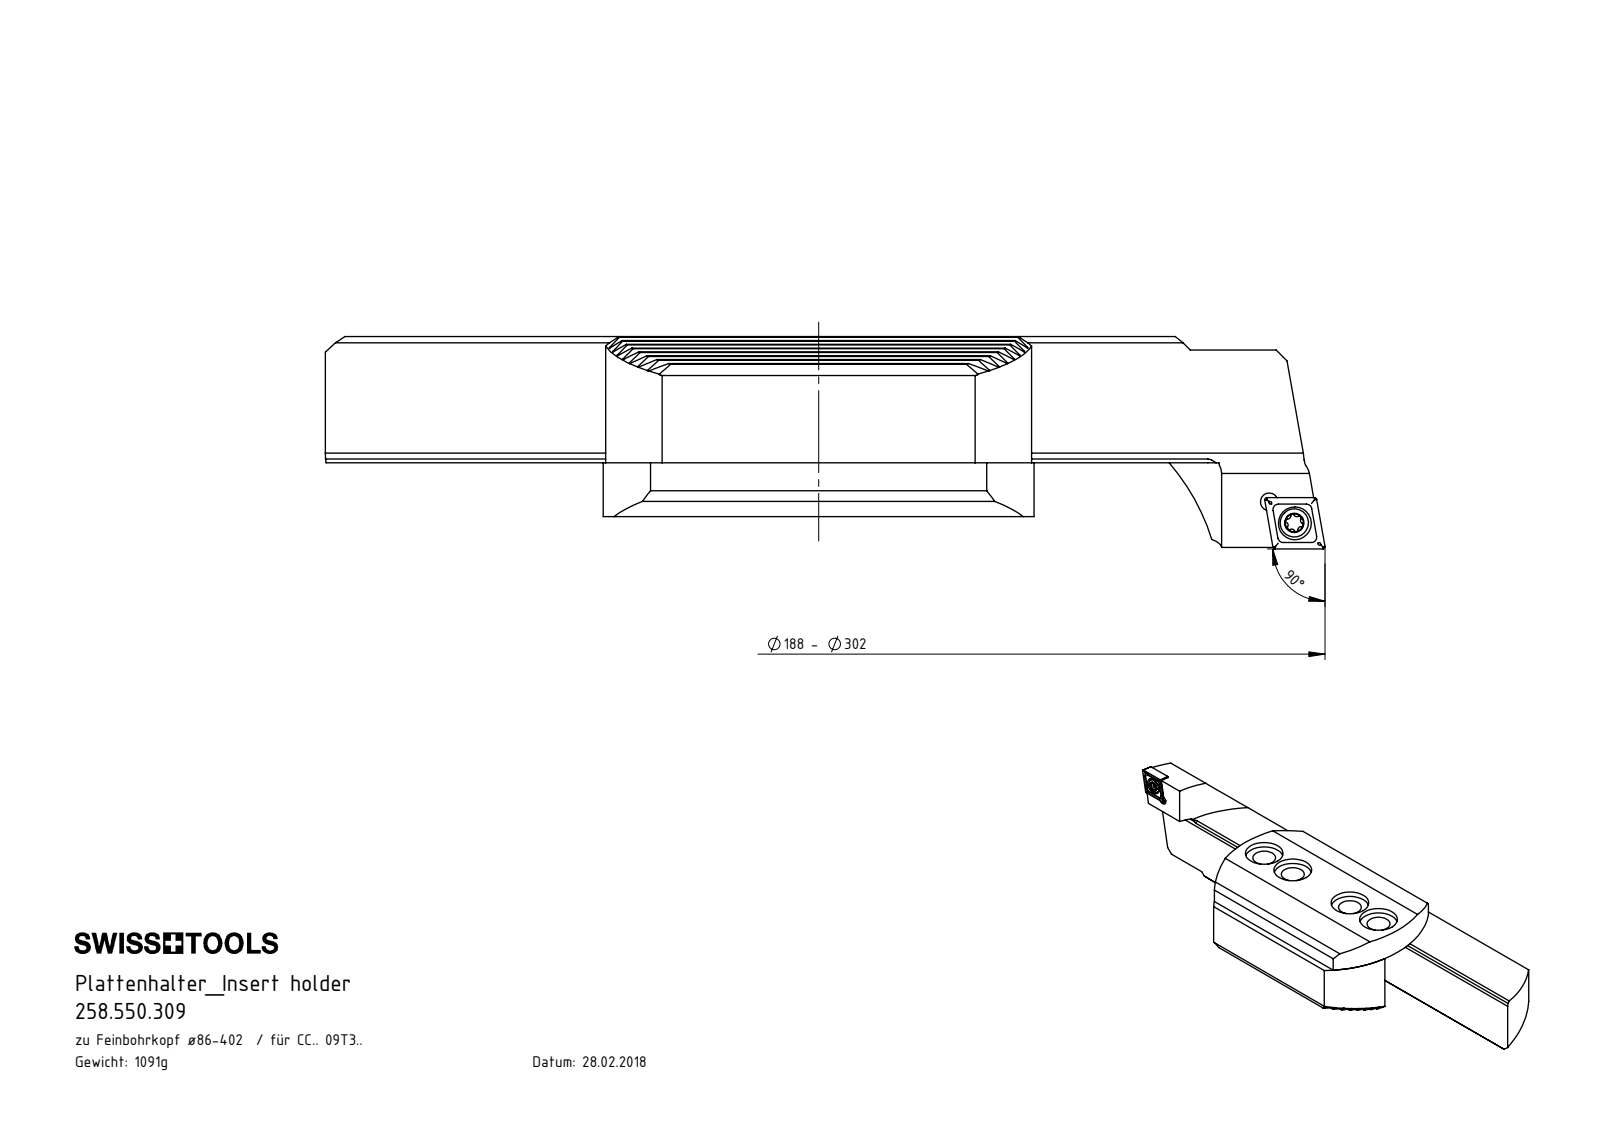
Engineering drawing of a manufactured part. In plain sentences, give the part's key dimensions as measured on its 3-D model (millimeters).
The part is named "F00-WCB.136.003_A; 258.550.309; CCMT09T304; WCB-ER2.001.009_A (+3 more)". Its 3-D file was written by "SolidWorks 2017 (CONFIG_CONTROL_DESIGN)". It is 5 solids with 770 faces: 462 planar, 67 cylindrical and 241 other. Overall it measures 185.57 by 55 by 39.4 millimeters. Its volume is 139 002 cubic millimeters and its surface area 36 711 square millimeters. Round holes: 4 of diameter 8.5, 4 of diameter 14, 2 of diameter 3.3, 1 of diameter 4.4, 1 of diameter 6.1. Round bosses or shafts: 1 of diameter 5.25, 1 of diameter 4. Partial cylindrical surfaces (rounded edges, fillets, slot ends): 16 of radius 0.2, 6 of radius 0.34, 6 of radius 0.59, 6 of radius 40, 1 of radius 0.8. The main face-to-face distances are 2.38, 4.76, 21.3, 33.7, 7.14, 9.52, 12.4, 4.77, 7.15, 9.53. The hole center spacings are 15, 45, 6.06, 6.19, 30, 60.
